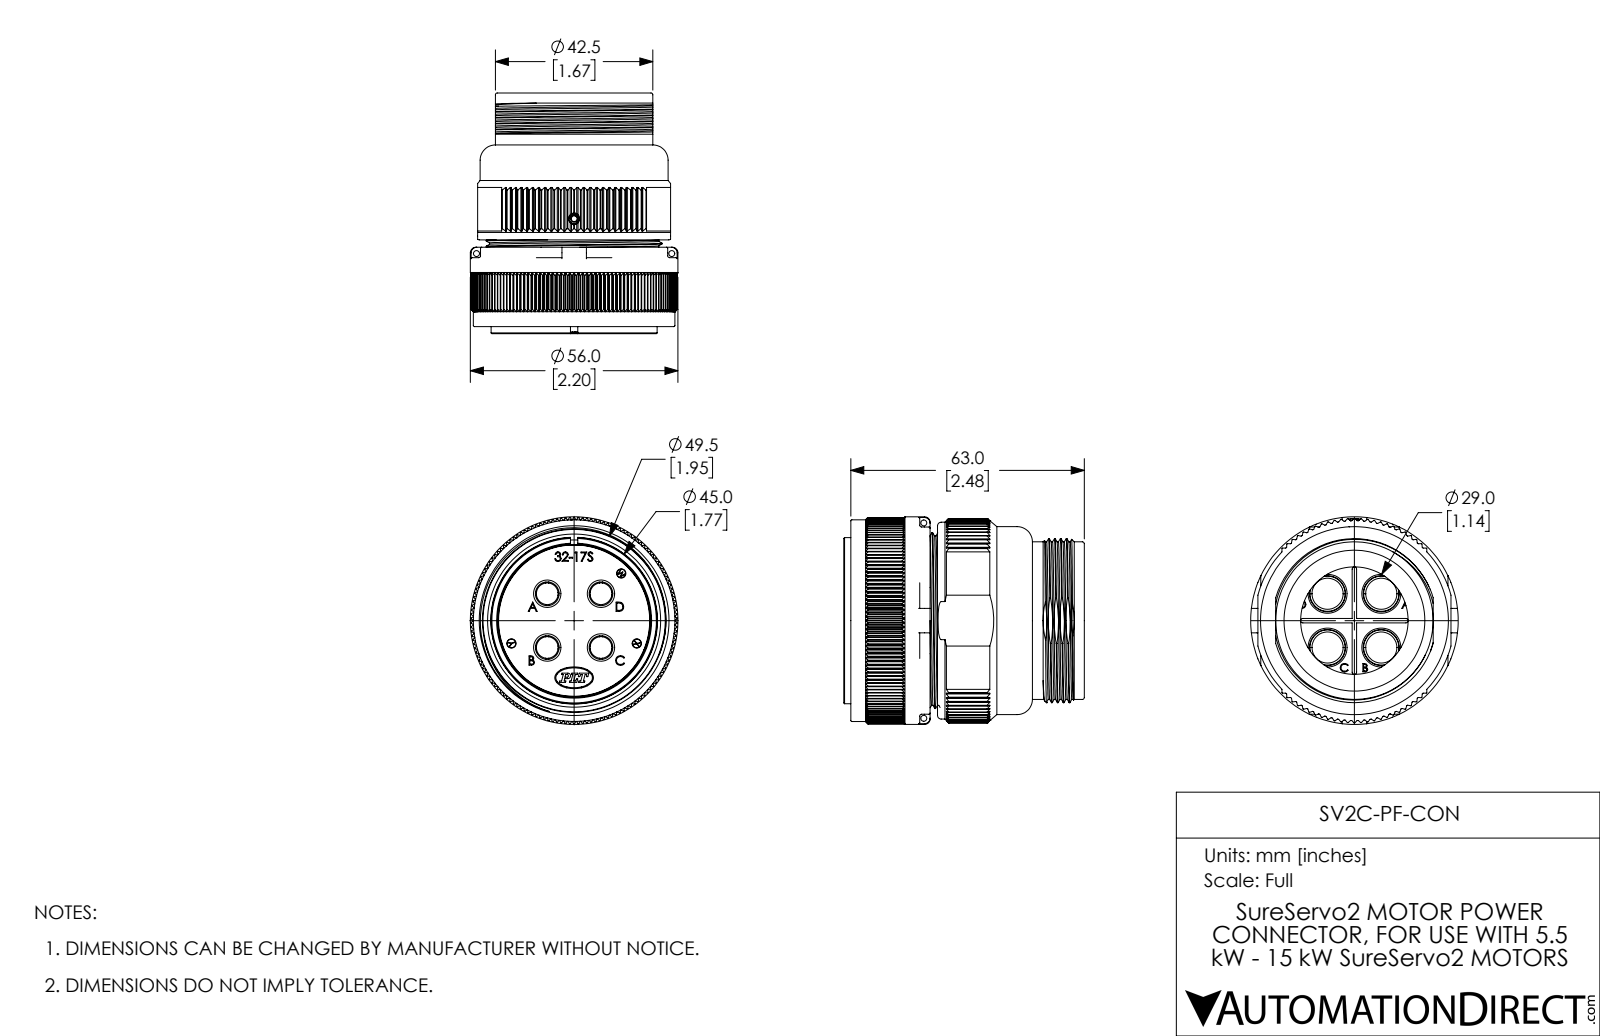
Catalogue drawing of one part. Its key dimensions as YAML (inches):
part_name: "PF-CON r1 coord fXT B"
step_written_by: "SolidWorks 2017 (AUTOMOTIVE_DESIGN)"
units: inches
bodies: {solids: 13, faces: 2136, planar: 928, cylindrical: 715, other: 493}
overall_size: [2.555, 2.205, 2.205]
volume: 4.991
surface_area: 98.04
round_holes:
  - {diameter: 0.091, count: 6}
  - {diameter: 0.063, count: 4}
  - {diameter: 0.23, count: 4}
  - {diameter: 0.252, count: 4}
  - {diameter: 0.331, count: 4}
  - {diameter: 0.382, count: 4}
  - {diameter: 0.386, count: 4}
  - {diameter: 0.413, count: 4}
  - {diameter: 0.433, count: 4}
  - {diameter: 0.097, count: 1}
  - {diameter: 0.11, count: 1}
  - {diameter: 0.118, count: 1}
round_bosses_or_shafts:
  - {diameter: 0.098, count: 6}
  - {diameter: 0.425, count: 4}
  - {diameter: 0.374, count: 4}
  - {diameter: 2.205, count: 1}
  - {diameter: 2.142, count: 1}
  - {diameter: 2.091, count: 1}
  - {diameter: 1.996, count: 1}
  - {diameter: 1.937, count: 1}
partial_cylinders:
  - {radius: 0.012, count: 12}
  - {radius: 0.02, count: 4}
  - {radius: 0.024, count: 4}
  - {radius: 0.142, count: 4}
  - {radius: 0.152, count: 4}
  - {radius: 0.233, count: 4}
  - {radius: 0.243, count: 4}
  - {radius: 0.061, count: 2}
face_to_face_distances: [0.63, 1.012, 1.331, 0.098, 0.319, 0.063, 0.031, 1.268, 0.161, 0.531]
hole_center_spacings: [0.404, 0.571, 0.033, 0.447, 0.65, 0.675, 0.709, 0.787]
